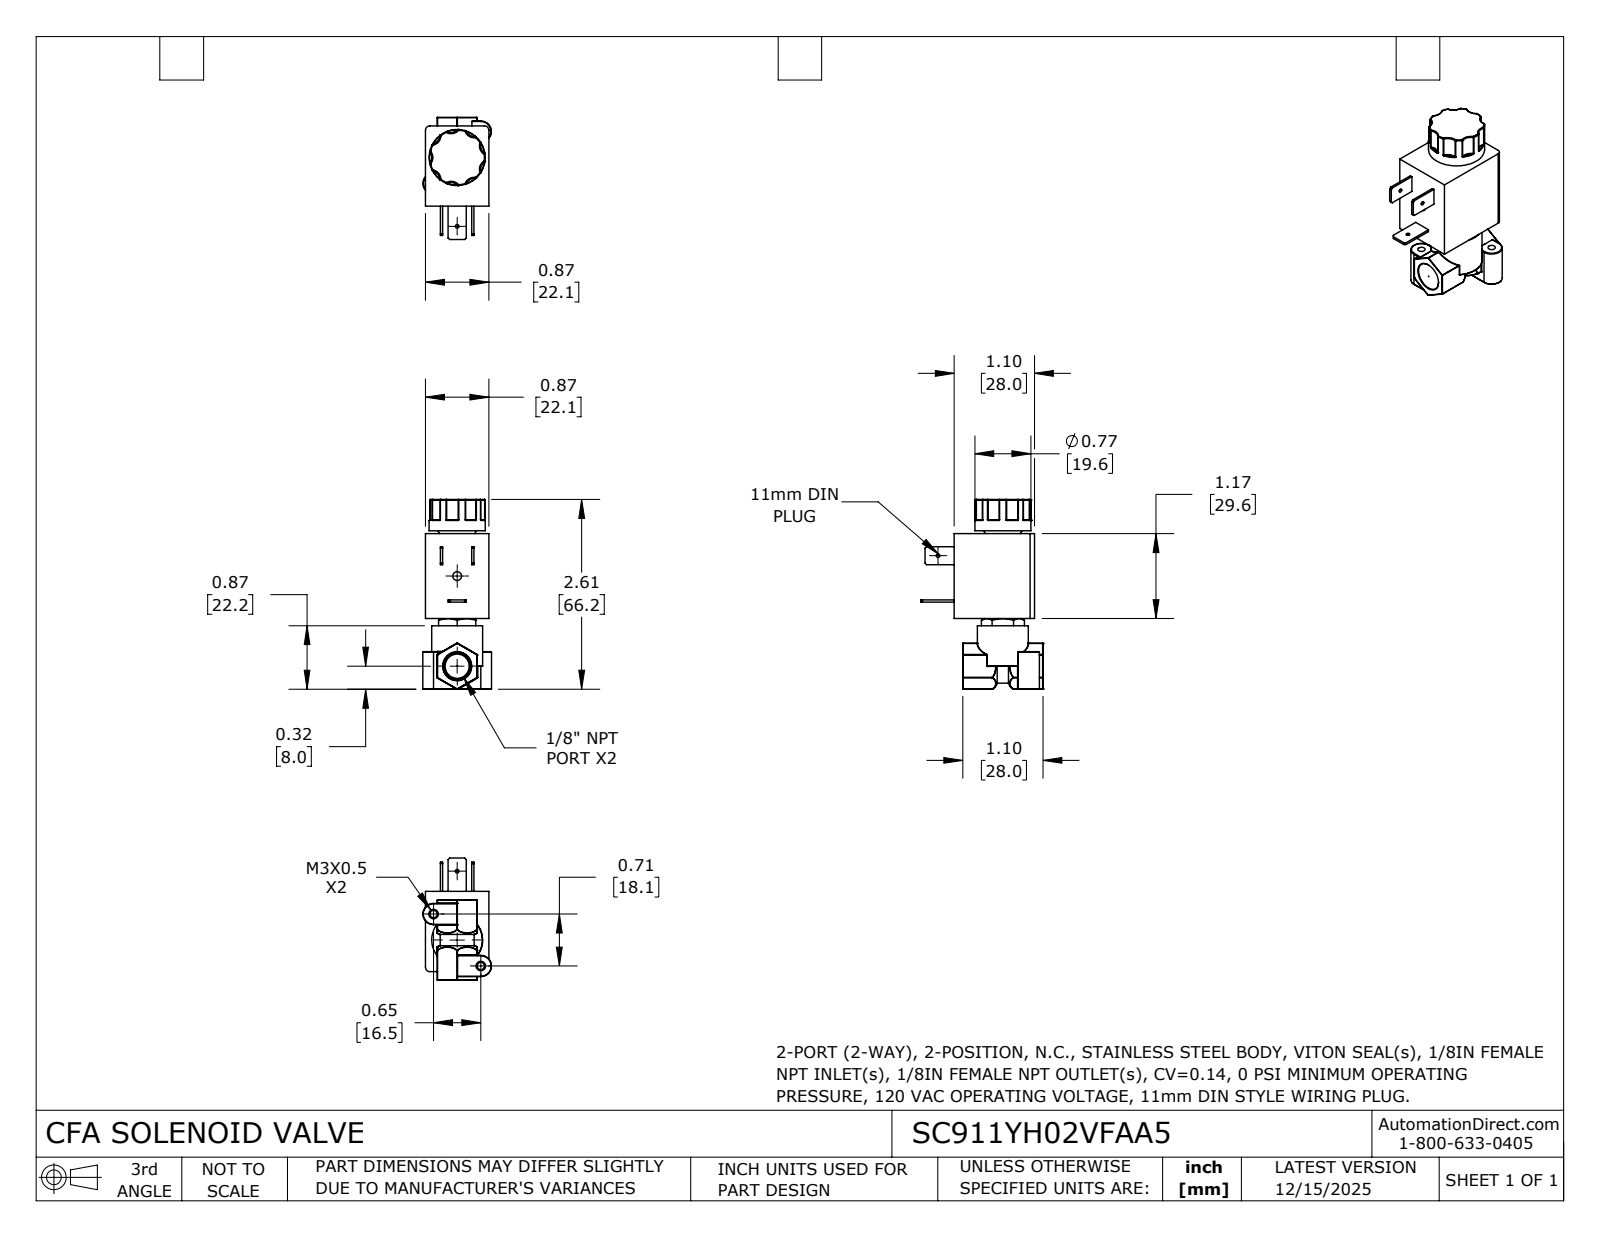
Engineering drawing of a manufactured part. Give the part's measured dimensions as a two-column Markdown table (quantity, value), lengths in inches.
| quantity | value |
| --- | --- |
| part name | SC911YH02VFAA5 |
| STEP written by | SolidWorks 2024 (CONFIG_CONTROL_DESIGN) |
| units | inches |
| bodies | 1 solid, 393 faces (76 planar, 108 cylindrical, 209 other) |
| overall size | 2.608 × 1.678 × 0.942 |
| volume | 1.713 in³ |
| surface area | 14.37 in² |
| round holes (diameter × count) | 0.05 × 2, 0.1 × 2, 0.12 × 1 |
| round bosses / shafts (diameter × count) | 0.77 × 1, 0.7 × 1, 0.332 × 1 |
| partial cylindrical surfaces (radius × count) | 0.004 × 27, 0.01 × 18, 0.008 × 12, 0.133 × 7, 0.017 × 2, 0.06 × 2, 0.132 × 2, 0.146 × 2 |
| main face-to-face distances | 0.87, 1.104, 1.167, 1.637, 0.47, 0.548, 0.161, 0.709, 1.207, 0.04 |
| hole center spacings | 0.672, 0.965, 1.342 |
